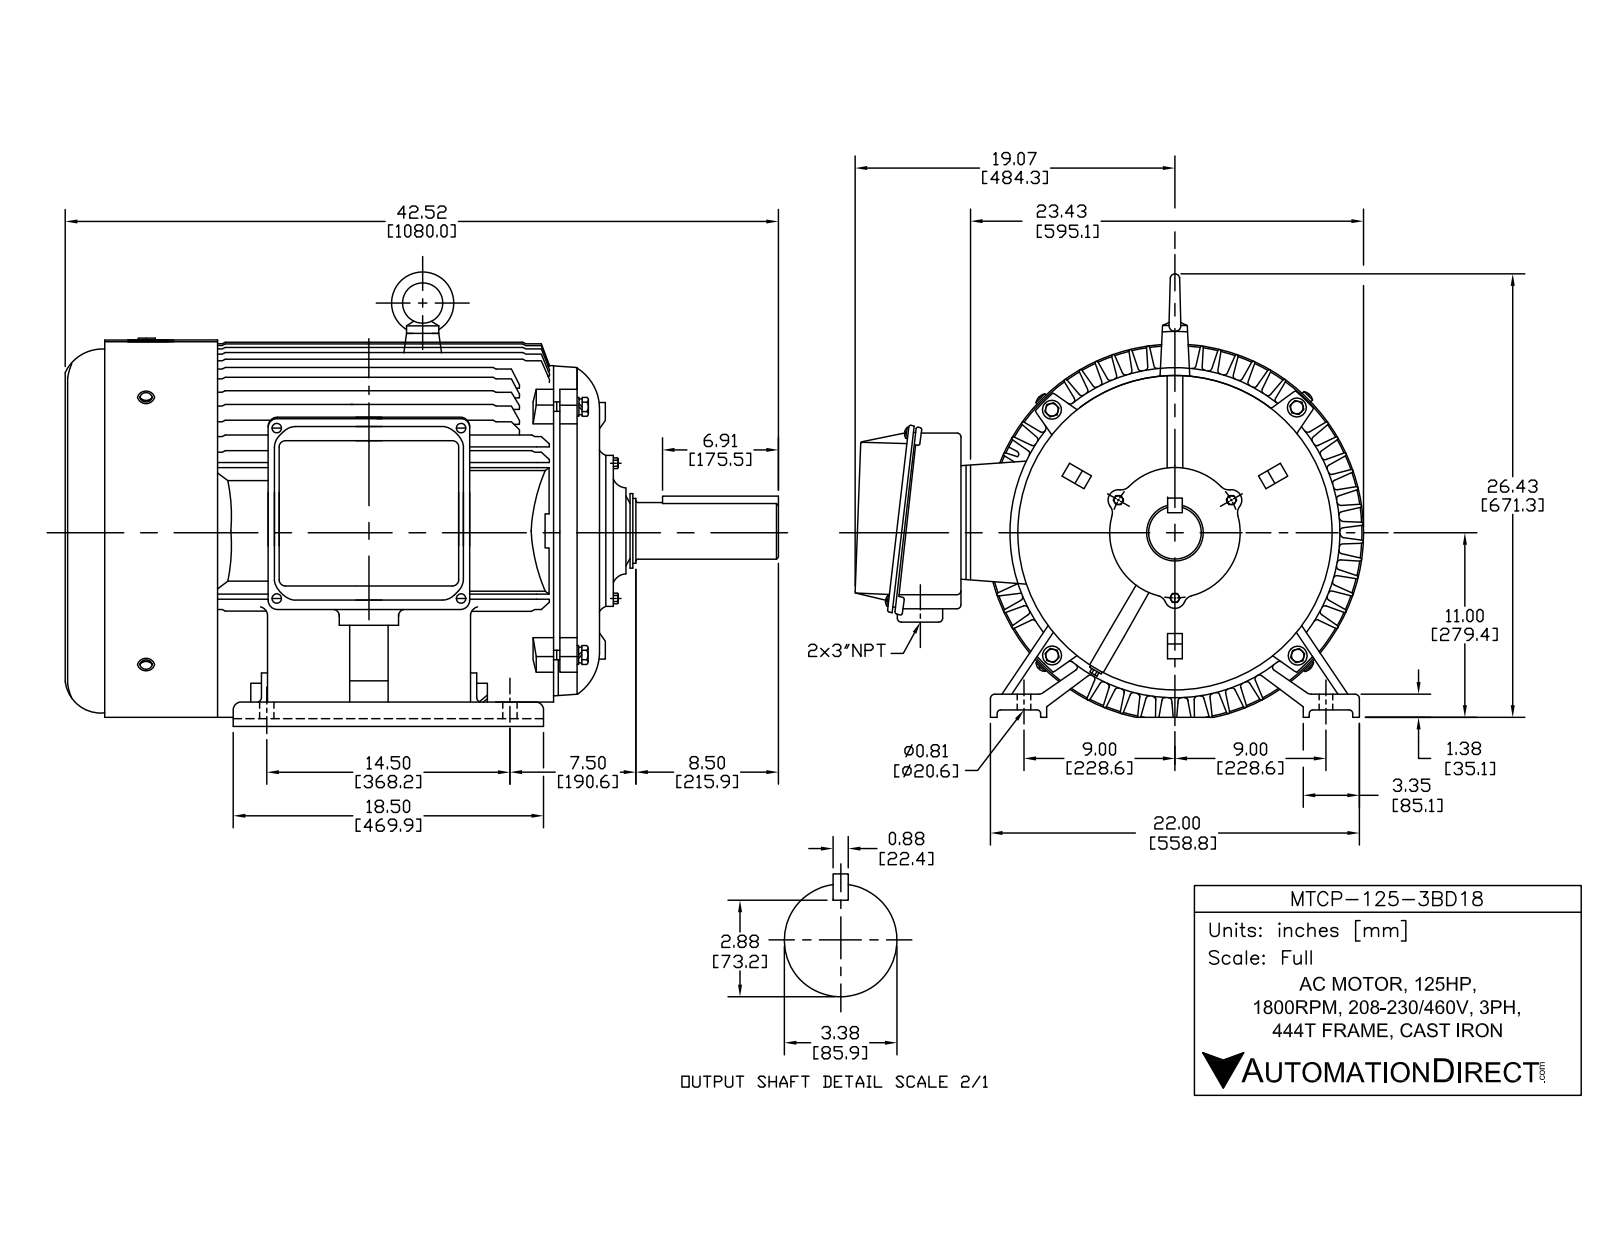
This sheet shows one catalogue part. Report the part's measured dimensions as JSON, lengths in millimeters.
{"part_name": "EP449接线盒座_默认_按加工; plain washers-chamfered--normal series-a gb_GB_FASTENER_WASHER_SWCA 8; EP444前轴承盖密封圈; hex head bolts-full thread grade c gb_GB_FASTENER_BOLT_HHBFTC M10X60-N (+8 more)", "step_written_by": "SolidWorks 2017 (AUTOMOTIVE_DESIGN)", "units": "millimeters", "bodies": {"solids": 68, "faces": 4381, "planar": 1214, "cylindrical": 1672, "other": 1495}, "overall_size": [1072.4, 780.96, 686.1], "volume_mm3": 37190000, "surface_area_mm2": 7176000, "round_holes": [[12, 20], [6.8, 8], [8.5, 8], [2.05, 4], [6, 4], [8.4, 4], [8.68, 4], [9, 4], [10, 4], [10.2, 4], [12.9, 4], [13, 4]], "round_bosses_or_shafts": [[10, 16], [24, 4], [19.1, 4], [16, 4], [12.88, 4], [12, 4], [8, 4], [584, 1]], "partial_cylinders_radius": [[1, 254], [3, 163], [5, 93], [2, 42], [9, 36], [6, 33], [10, 25], [0.75, 24]], "face_to_face_distances": [6, 2, 9, 14.7, 808.9, 806.9, 37.3, 817.9, 815.9, 40], "hole_center_spacings": [130, 87.5, 107.5, 99.03, 268, 20, 118.56, 134]}
